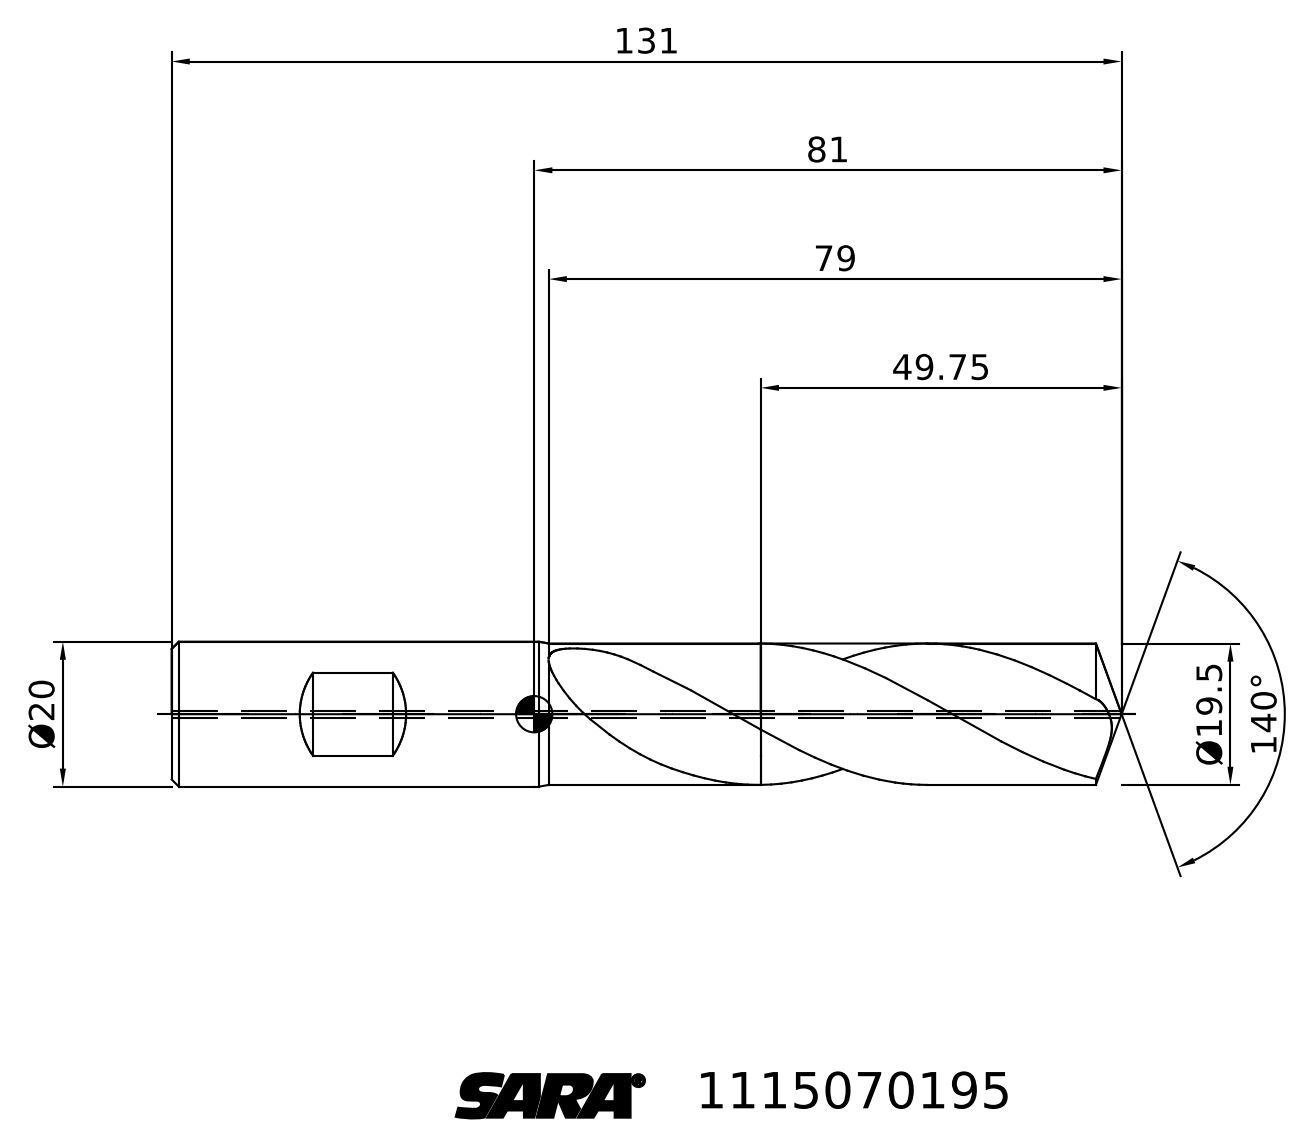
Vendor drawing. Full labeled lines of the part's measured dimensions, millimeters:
STEP written by: TDM (AUTOMOTIVE_DESIGN)
Units: millimetres
Bodies: 2 solids, 28 faces (6 planar, 0 cylindrical, 22 other)
Overall size (bounding box): 131 × 51.54 × 29.68
Volume: 31 811 mm³ · Surface area: 9 209 mm²
Main face-to-face distances: 81.25
